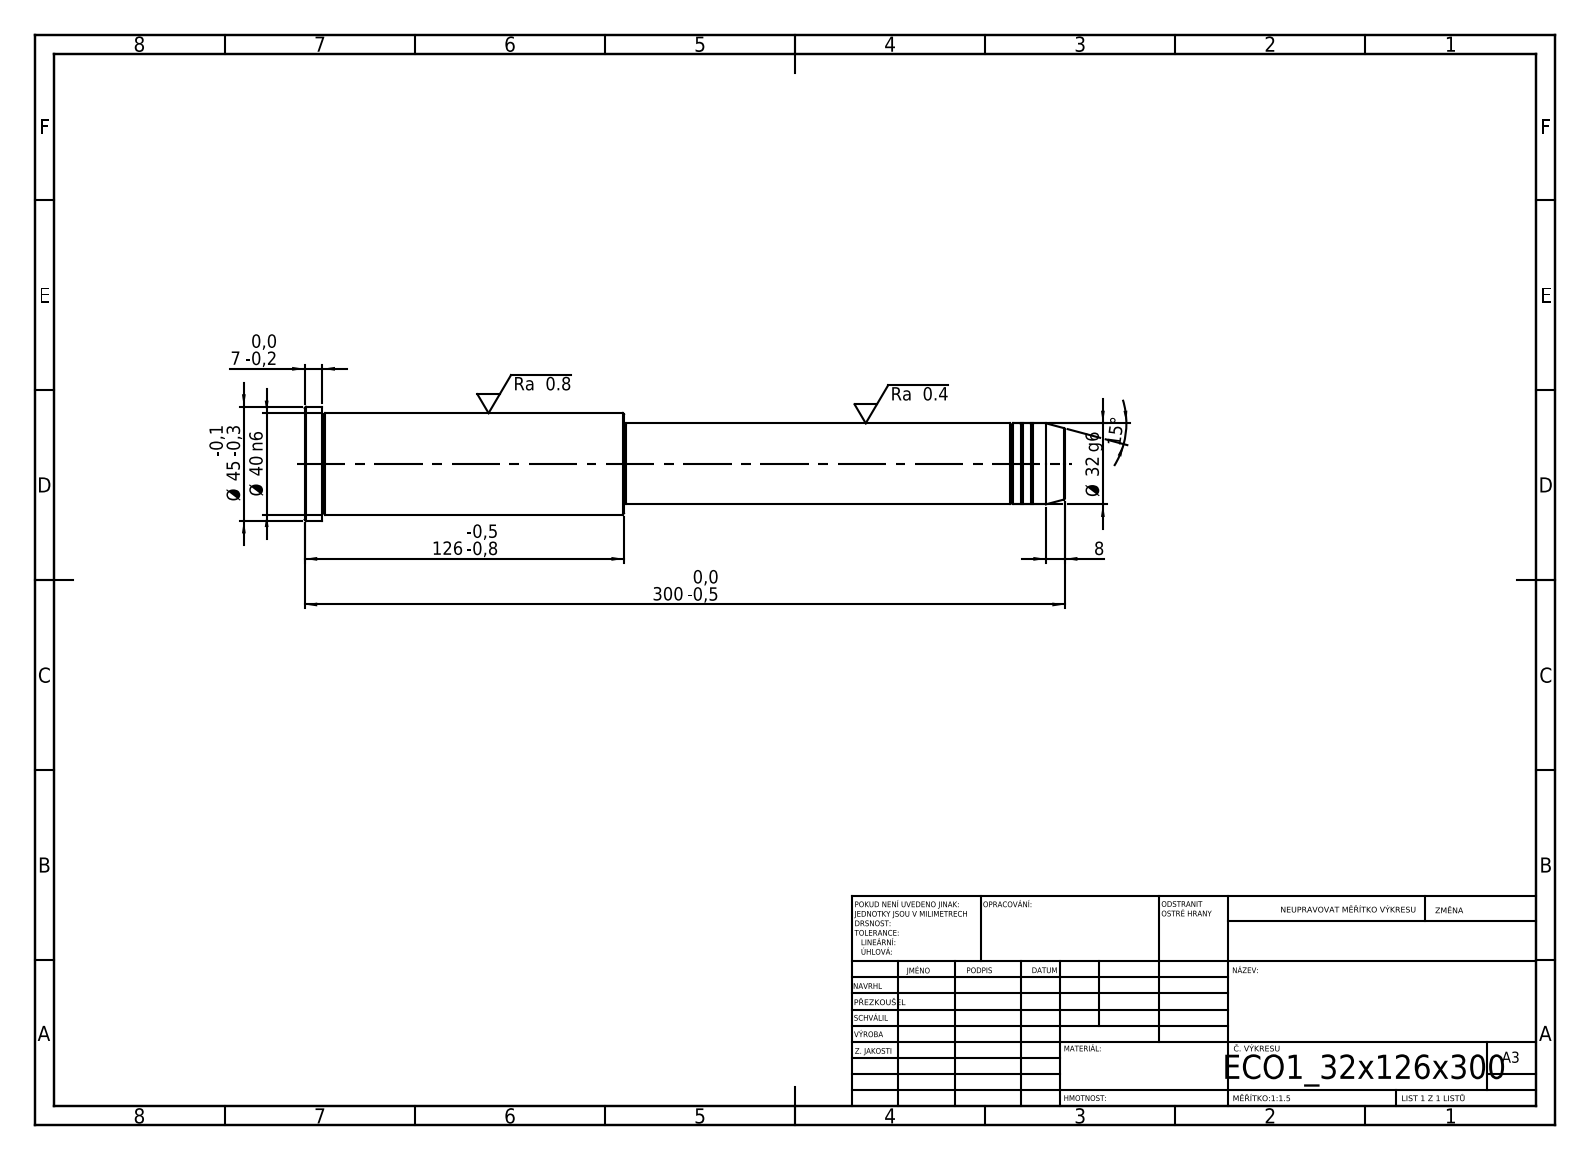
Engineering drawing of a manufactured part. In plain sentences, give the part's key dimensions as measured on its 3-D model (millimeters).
Its 3-D file was written by "SolidWorks 2019 (CONFIG_CONTROL_DESIGN)". It is 1 solid with 43 faces: 5 planar, 14 cylindrical and 24 other. Overall it measures 300 by 45 by 45 millimeters. Its volume is 299 635 cubic millimeters and its surface area 36 643 square millimeters. Round bosses or shafts: 1 of diameter 45, 1 of diameter 40, 1 of diameter 32, 1 of diameter 31. The main face-to-face distances are 300, 174, 126, 293, 119, 7, 173, 1, 120, 127.
